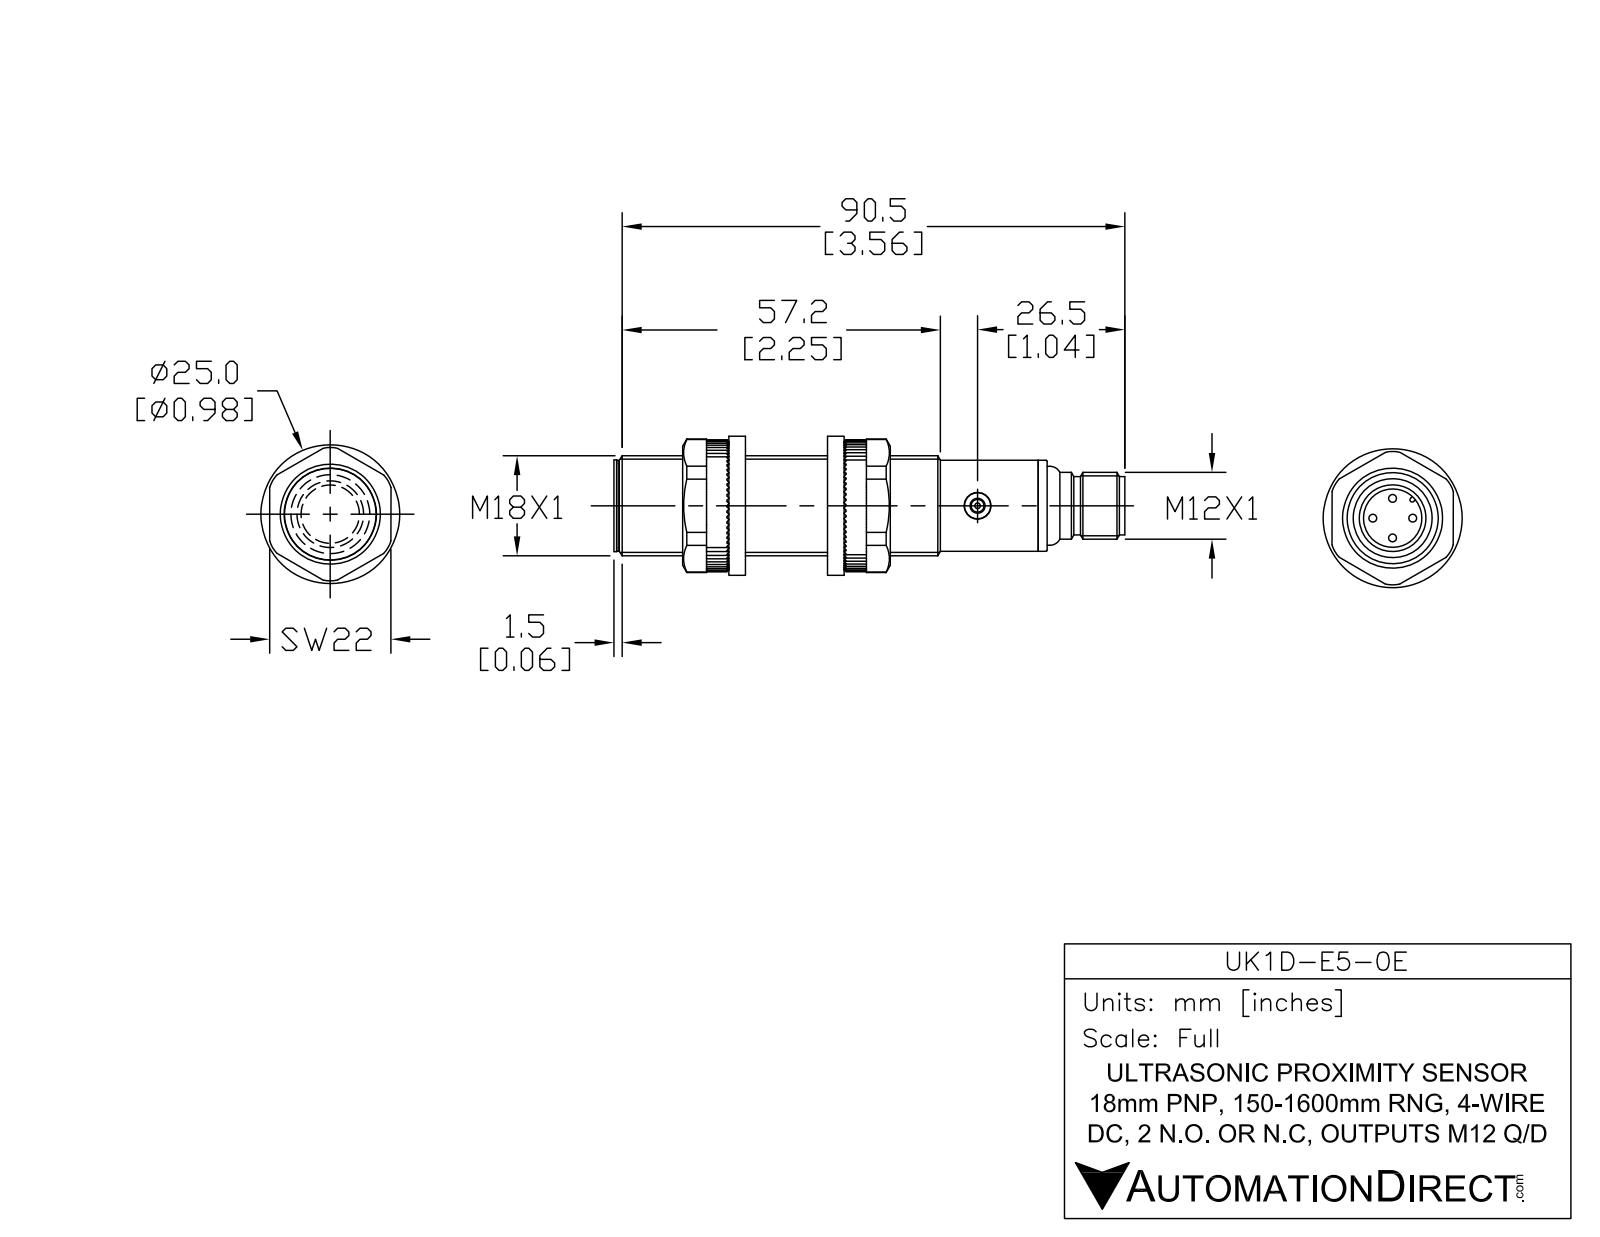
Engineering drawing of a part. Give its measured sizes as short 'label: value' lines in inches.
name: UK1D-E5-0E
written by: SolidWorks 2017 (AUTOMOTIVE_DESIGN)
unit: in
bodies: 6 solids, 106 faces (21 planar, 48 cylindrical, 37 other)
size: 3.606 × 0.709 × 0.709
volume: 1.202 in³; area: 10.68 in²
holes: 1× ⌀0.106, 1× ⌀0.185, 1× ⌀0.276, 1× ⌀0.327, 1× ⌀0.374
bosses: 4× ⌀0.039, 1× ⌀0.709, 1× ⌀0.654, 1× ⌀0.646, 1× ⌀0.622, 1× ⌀0.559, 1× ⌀0.472, 1× ⌀0.413
rounds: 1× R0.024
face distances: 2.957, 0.039, 2.996, 0.037, 2.994, 0.043, 0.157, 3.055, 3.053, 3.016
